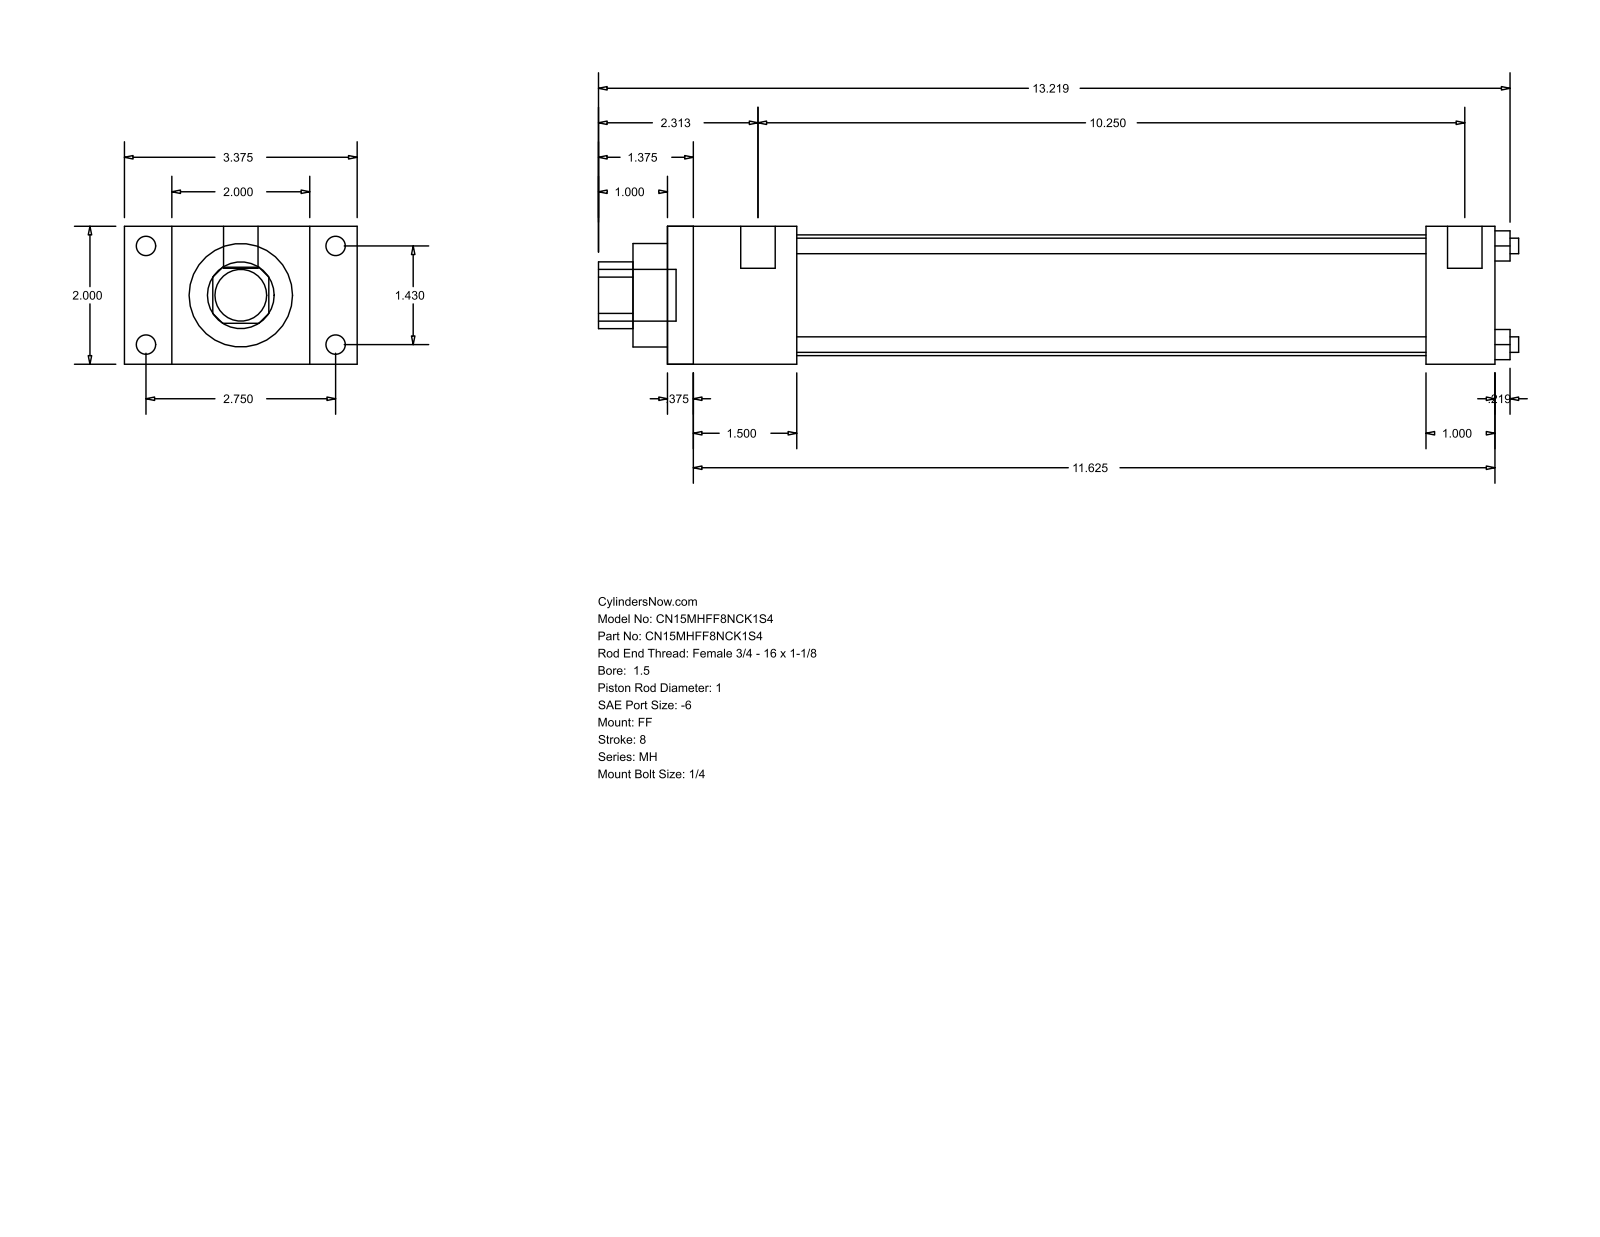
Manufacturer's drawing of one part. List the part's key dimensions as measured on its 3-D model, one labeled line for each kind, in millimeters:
Part name (STEP PRODUCT): MH_FF__0150_1
STEP written by: GSSL Pune (CONFIG_CONTROL_DESIGN)
Units: millimetres
Bodies: 0 solids, 92 faces (64 planar, 28 cylindrical, 0 other)
Overall size (bounding box): 338.93 × 85.72 × 50.8
Round holes (diameter × count): ⌀5.71 ×4, ⌀25.4 ×1, ⌀38.1 ×1, ⌀44.45 ×1
Round bosses / shafts (diameter × count): ⌀7.14 ×4, ⌀5.56 ×4, ⌀12.7 ×2, ⌀19.05 ×1
Partial cylindrical surfaces — rounded edges, fillets, slot ends (radius × count): R12.29 ×1
Main face-to-face distances: 50.8, 304.8, 9.52, 295.28, 25.4, 17.46, 68.26, 47.63, 38.11, 257.17
Hole centre spacings: 25.68, 36.32, 51.36
